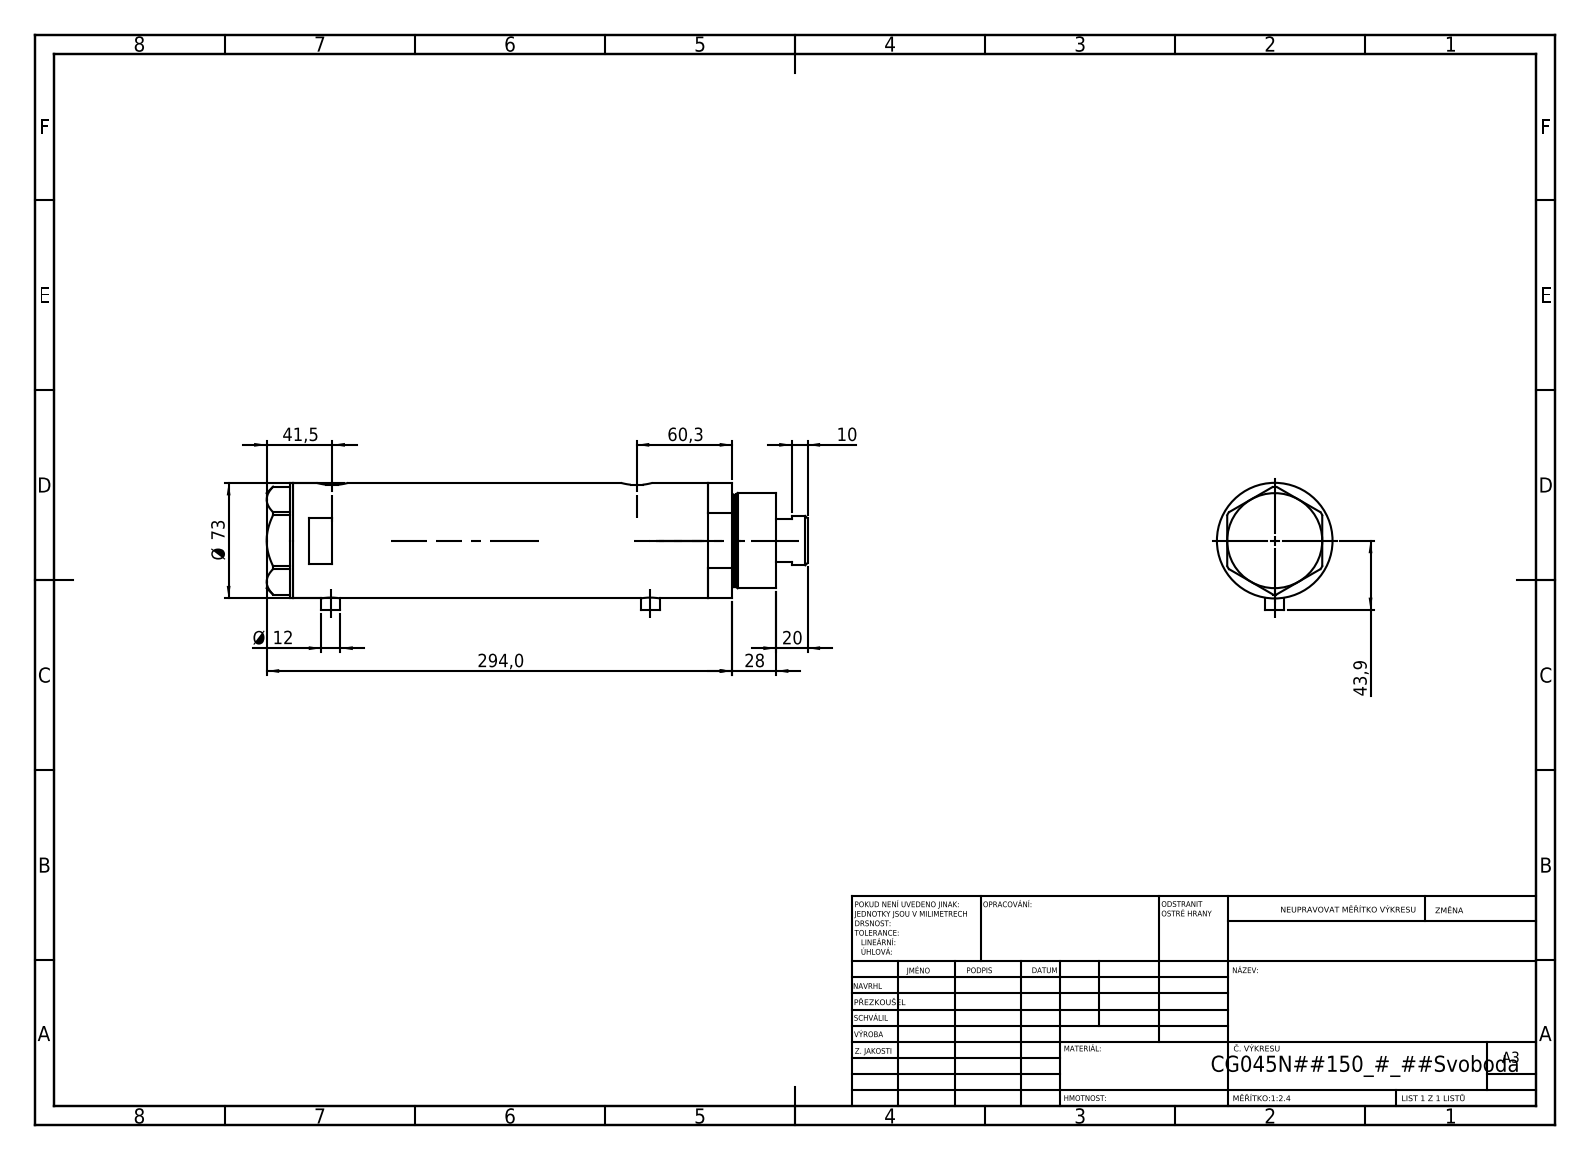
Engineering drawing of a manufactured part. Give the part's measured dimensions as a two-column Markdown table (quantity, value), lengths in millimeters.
| quantity | value |
| --- | --- |
| part name | V270CG_BACK; V270CG_FRONT; V270CG_MIDDLE; V270CG_VC |
| STEP written by | SolidWorks 2019 (CONFIG_CONTROL_DESIGN) |
| units | millimeters |
| bodies | 4 solids, 125 faces (50 planar, 55 cylindrical, 20 other) |
| overall size | 341.52 × 80.4 × 73 |
| volume | 1 178 000 mm³ |
| surface area | 191 299 mm² |
| round holes (diameter × count) | 5 × 2, 12.5 × 2, 13.16 × 2, 10.5 × 1, 32 × 1, 33.5 × 1, 45 × 1, 48 × 1, 64 × 1 |
| round bosses / shafts (diameter × count) | 12 × 2, 73 × 1, 60 × 1, 58 × 1, 31 × 1 |
| partial cylindrical surfaces (radius × count) | 10 × 2 |
| main face-to-face distances | 191.15, 42.5, 233.65, 16.5, 16.51, 26, 217.15, 25.99, 217.14, 2 |
| hole center spacings | 201.65, 0.99, 1, 8.5, 8.51, 192.15, 193.14, 193.15 |
